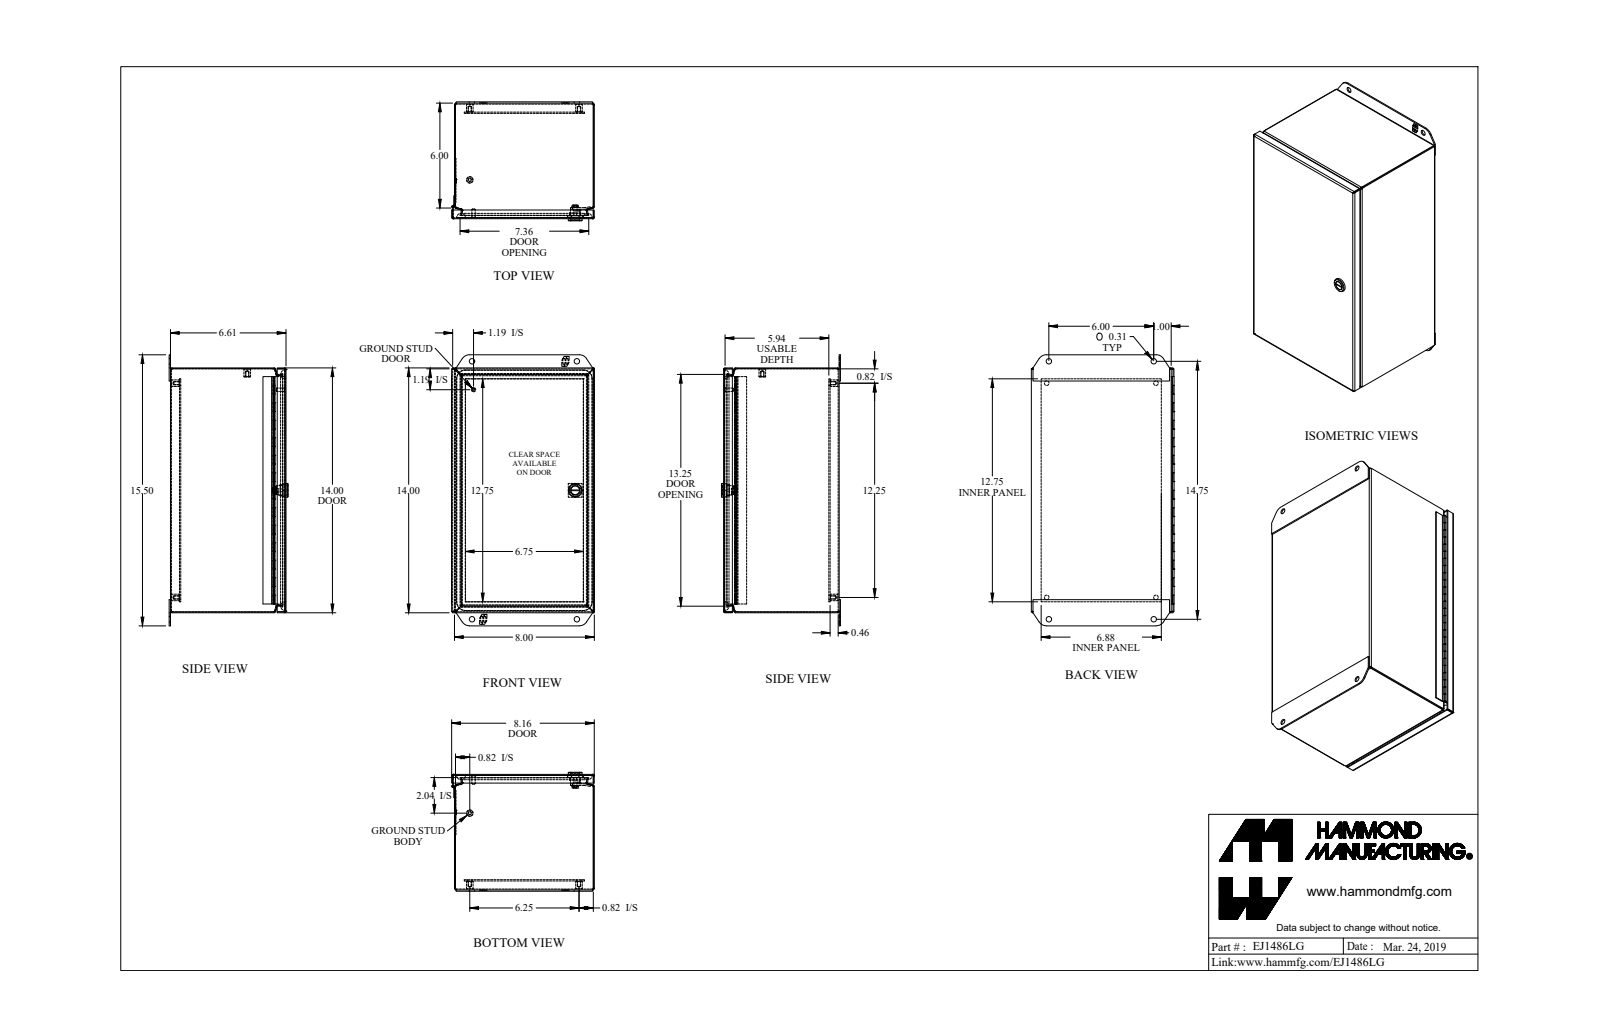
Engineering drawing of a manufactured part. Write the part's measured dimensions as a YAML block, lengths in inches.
part_name: "EJ1486LG_Default"
step_written_by: "SolidWorks 2019 (CONFIG_CONTROL_DESIGN)"
units: inches
bodies: {solids: 16, faces: 739, planar: 409, cylindrical: 238, other: 92}
overall_size: [15.5, 8.165, 6.805]
volume: 43.32
surface_area: 1440
round_holes:
  - {diameter: 0.156, count: 5}
  - {diameter: 0.265, count: 4}
  - {diameter: 0.313, count: 4}
  - {diameter: 0.05, count: 1}
  - {diameter: 0.516, count: 1}
round_bosses_or_shafts:
  - {diameter: 0.375, count: 5}
  - {diameter: 0.788, count: 1}
  - {diameter: 0.535, count: 1}
  - {diameter: 0.496, count: 1}
  - {diameter: 0.435, count: 1}
  - {diameter: 0.25, count: 1}
  - {diameter: 0.188, count: 1}
  - {diameter: 0.1, count: 1}
partial_cylinders:
  - {radius: 0.029, count: 16}
  - {radius: 0.086, count: 16}
  - {radius: 0.281, count: 10}
  - {radius: 0.25, count: 4}
  - {radius: 0.499, count: 4}
  - {radius: 0.5, count: 4}
  - {radius: 0.06, count: 2}
  - {radius: 0.539, count: 2}
face_to_face_distances: [0.057, 6.554, 7.943, 6.611, 0.072, 0.589, 6.497, 13.943, 0.46, 0.517]
hole_center_spacings: [14.824, 1.256, 1.257, 6, 6.129, 6.25, 6.251, 6.252]
